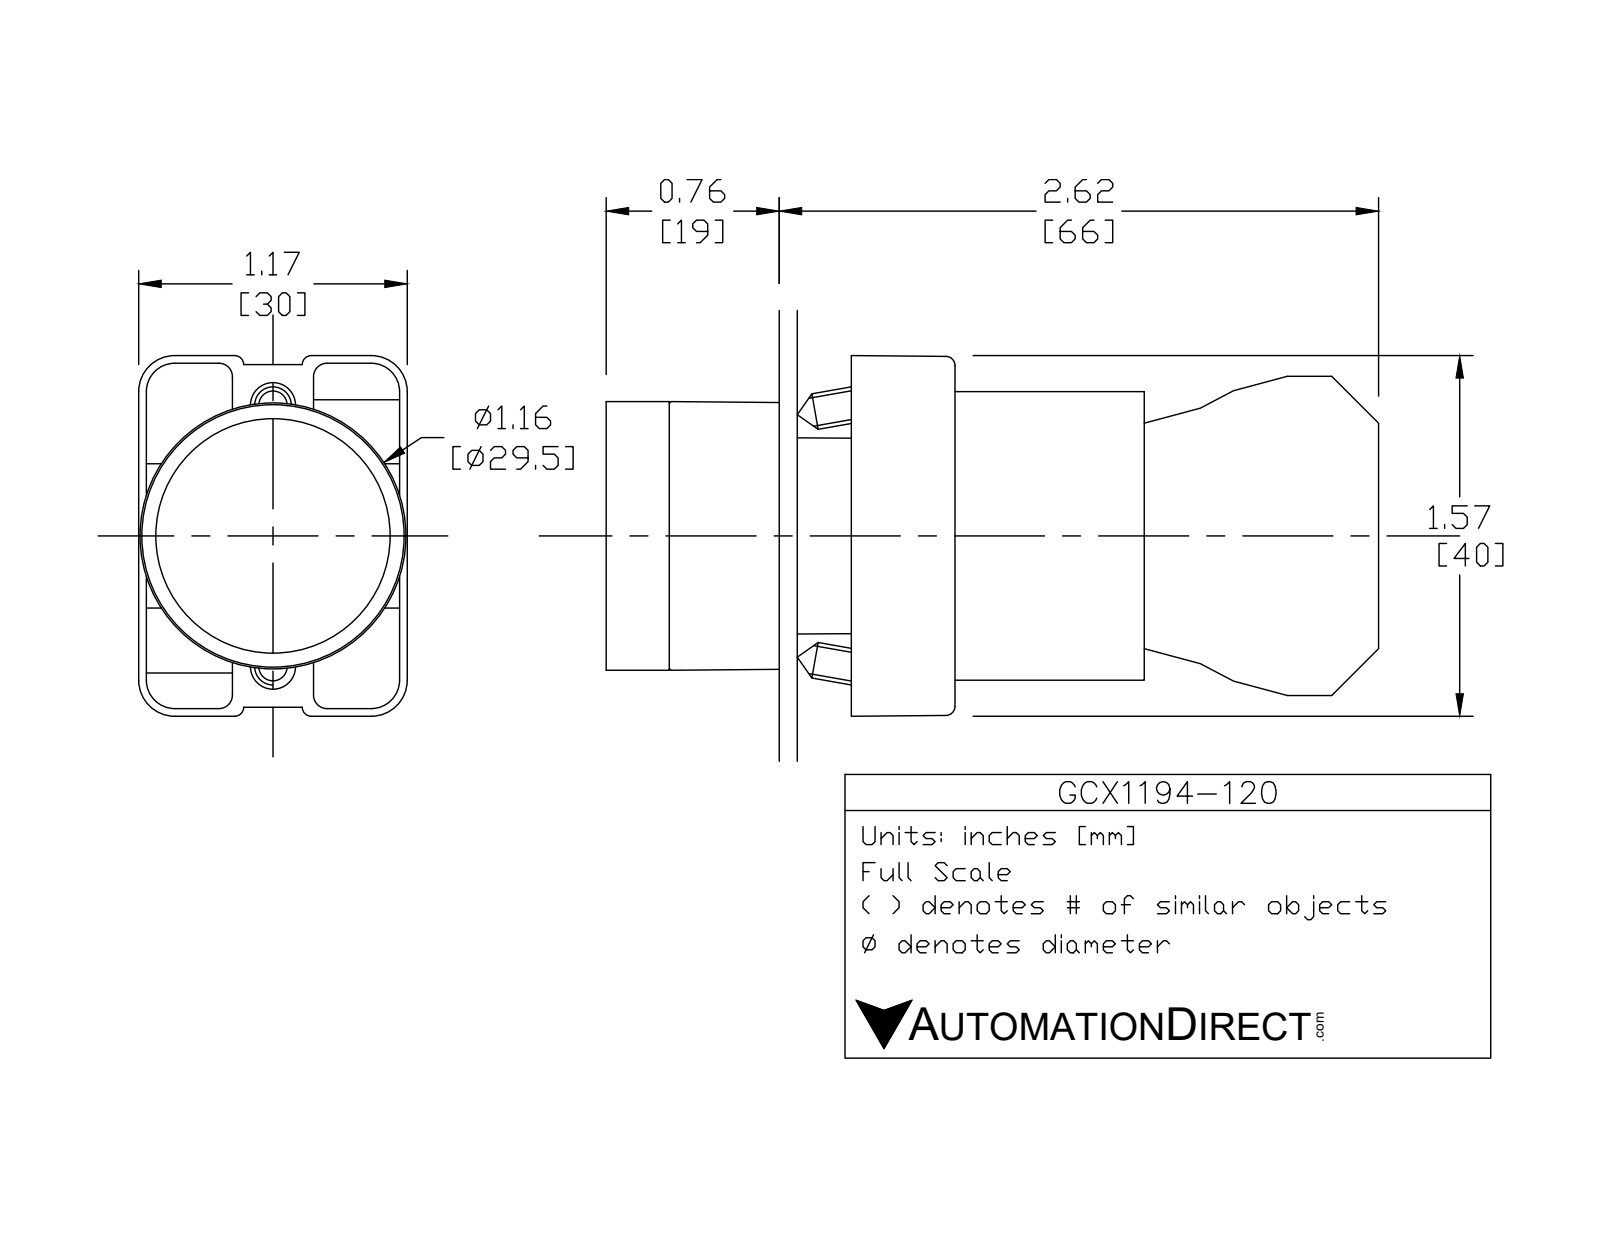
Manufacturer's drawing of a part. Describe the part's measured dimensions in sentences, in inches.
The part is named "GCX1194 OPERATOR; ecx1040; ECX1050; GCX1194-120 (+1 more)". Its 3-D file was written by "SolidWorks 2016 (AUTOMOTIVE_DESIGN)". It is 8 solids with 431 faces: 252 planar, 148 cylindrical and 31 other. Overall it measures 3.319 by 1.581 by 1.177 inches. Its volume is 2.794 cubic inches and its surface area 38.75 square inches. Round holes: 2 of diameter 0.079, 2 of diameter 0.124, 2 of diameter 0.13, 1 of diameter 0.087, 1 of diameter 0.197, 1 of diameter 0.469, 1 of diameter 0.878, 1 of diameter 0.888, 1 of diameter 1.024. Round bosses or shafts: 4 of diameter 0.157, 1 of diameter 1.175, 1 of diameter 1.004, 1 of diameter 0.945, 1 of diameter 0.856, 1 of diameter 0.78, 1 of diameter 0.504. Partial cylindrical surfaces (rounded edges, fillets, slot ends): 24 of radius 0.059, 12 of radius 0.041, 12 of radius 0.124, 12 of radius 0.157, 8 of radius 0.039, 2 of radius 0.128, 1 of radius 0.02, 1 of radius 0.063. The main face-to-face distances are 0.827, 2.02, 1.193, 0.579, 1.171, 0.031, 0.276, 0.033, 0.748, 0.573. The hole center spacings are 0.236, 0.544, 0.472, 0.49.
